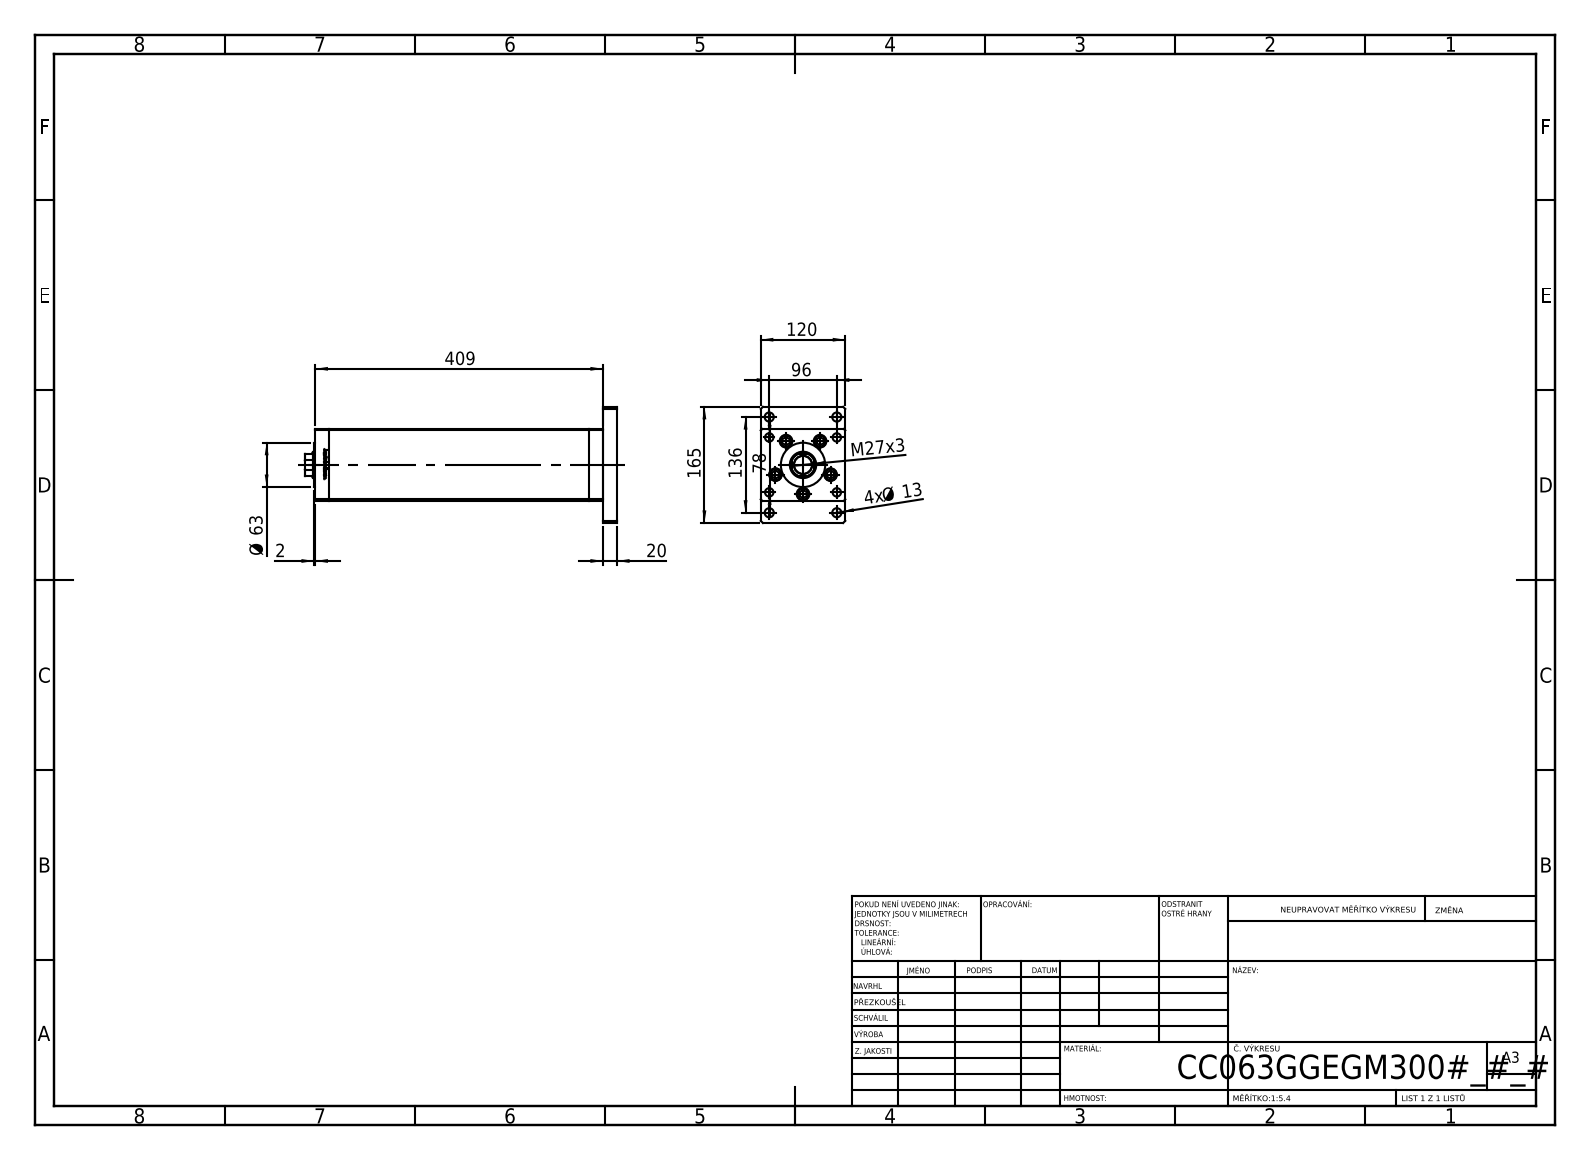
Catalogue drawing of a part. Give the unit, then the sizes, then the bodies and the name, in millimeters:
Units: millimetres
Overall size (bounding box): 443.5 × 165 × 120
Round holes (diameter × count): ⌀12 ×9, ⌀13.5 ×5, ⌀18 ×5, ⌀13 ×4, ⌀17 ×4, ⌀2 ×2, ⌀13.16 ×2, ⌀25.5 ×1, ⌀36 ×1, ⌀37.5 ×1, ⌀83 ×1
Round bosses / shafts (diameter × count): ⌀8 ×9, ⌀17 ×5, ⌀63 ×1
Partial cylindrical surfaces — rounded edges, fillets, slot ends (radius × count): R0.93 ×2, R17.5 ×1
Main face-to-face distances: 20, 120, 102, 388.5, 408.5, 368.5, 40, 2, 406.5, 18
Hole centre spacings: 41.5, 29, 61.85, 83.23, 96, 100.28, 107, 143.75
Volume: 4 581 000 mm³ · Surface area: 488 863 mm²
Bodies: 19 solids, 1313 faces (518 planar, 189 cylindrical, 606 other)
Part name (STEP PRODUCT): ALLEN BOLT; V220C_F; V220C_G_MIDDLE; V220C_VC_G (+2 more)
STEP written by: SolidWorks 2019 (CONFIG_CONTROL_DESIGN)
